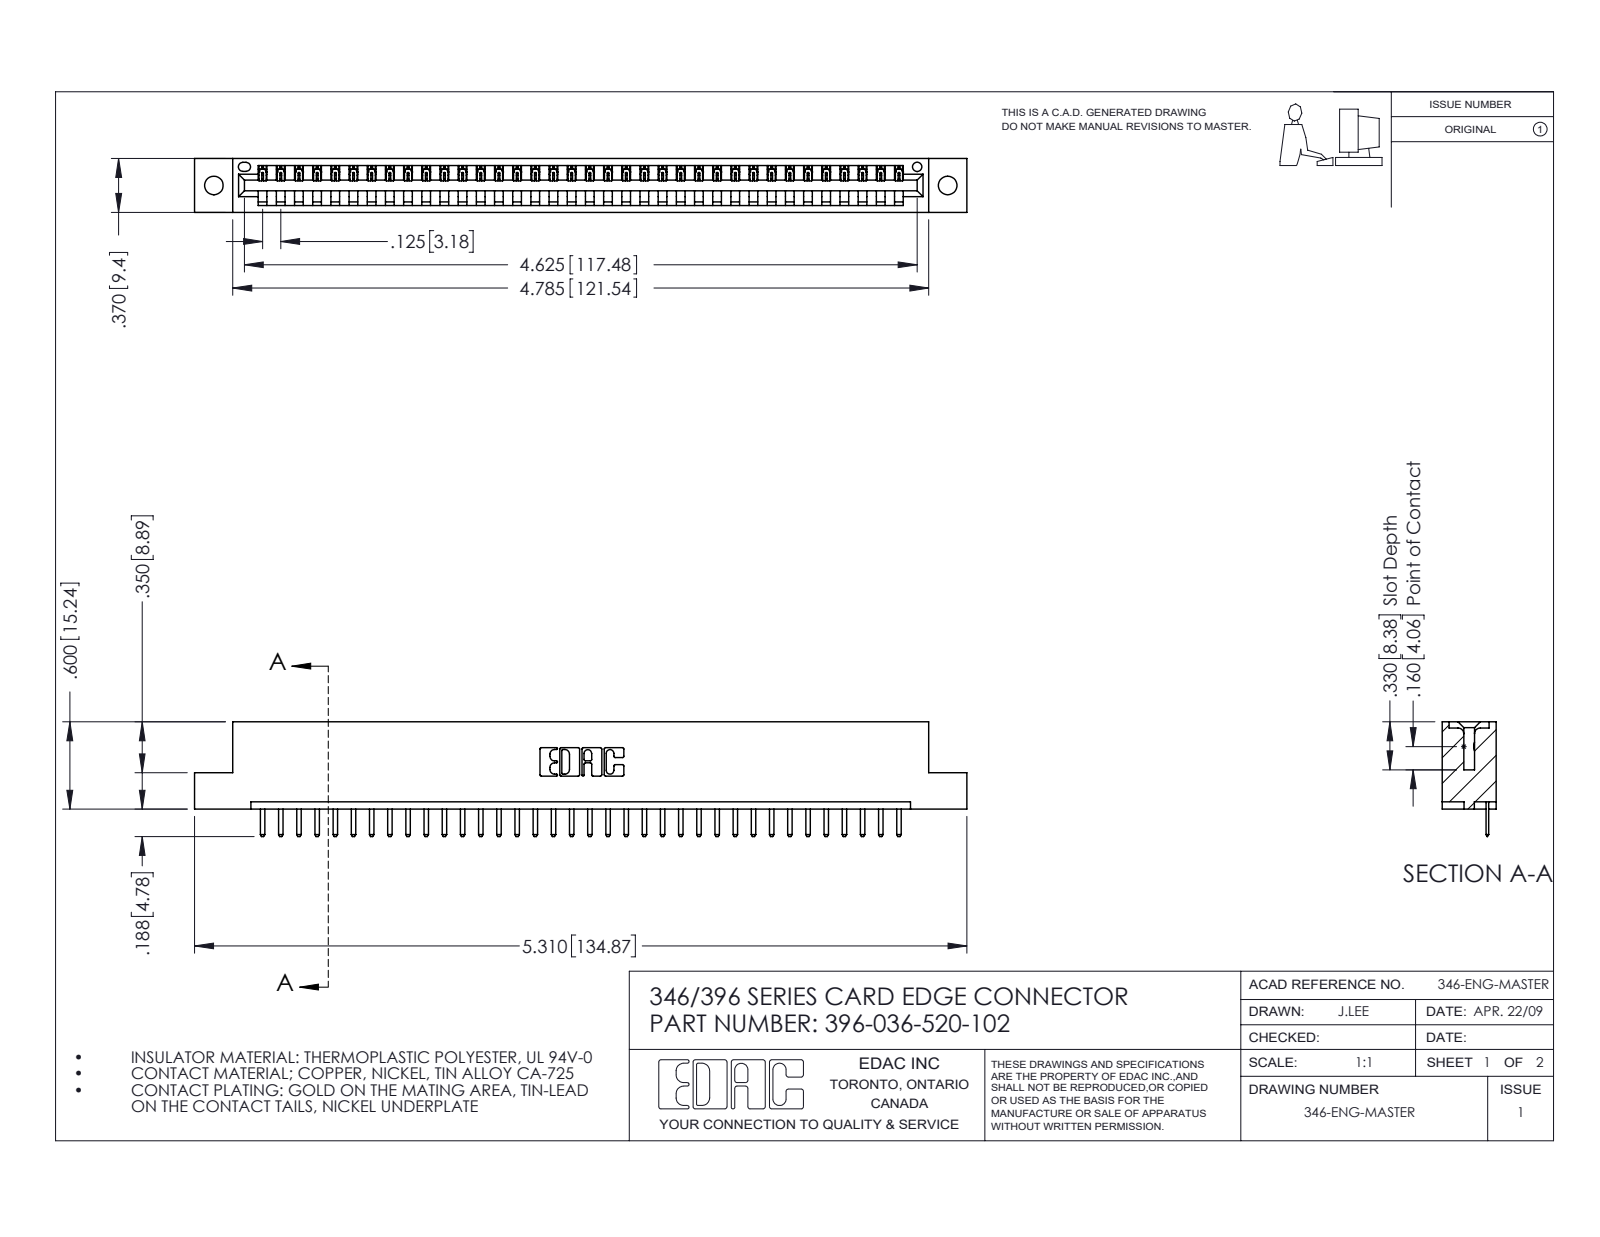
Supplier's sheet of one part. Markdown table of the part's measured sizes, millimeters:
| quantity | value |
| --- | --- |
| part name | 396-036-520-102; 346 Part_Flush Mounting Lugs - 0.128 Dia; 345-292-001_345-293-120 |
| STEP written by | SolidWorks 2016 (CONFIG_CONTROL_DESIGN) |
| units | millimeters |
| bodies | 37 solids, 2354 faces (1588 planar, 766 cylindrical, 0 other) |
| overall size | 134.9 × 20 × 9.4 |
| volume | 12 700 mm³ |
| surface area | 15 230 mm² |
| round holes (diameter × count) | 3.3 × 2, 1.6 × 1 |
| partial cylindrical surfaces (radius × count) | 0.3 × 74, 0.2 × 72, 0.3 × 22, 0.2 × 6, 0.8 × 6, 0.7 × 3, 0.8 × 2, 1 × 2 |
| main face-to-face distances | 1.2, 8.2, 9.4, 6.4, 3.8, 5.6, 2.5, 4.4, 1.8, 7.6 |
| hole center spacings | 6.2, 122.8, 128.1 |
